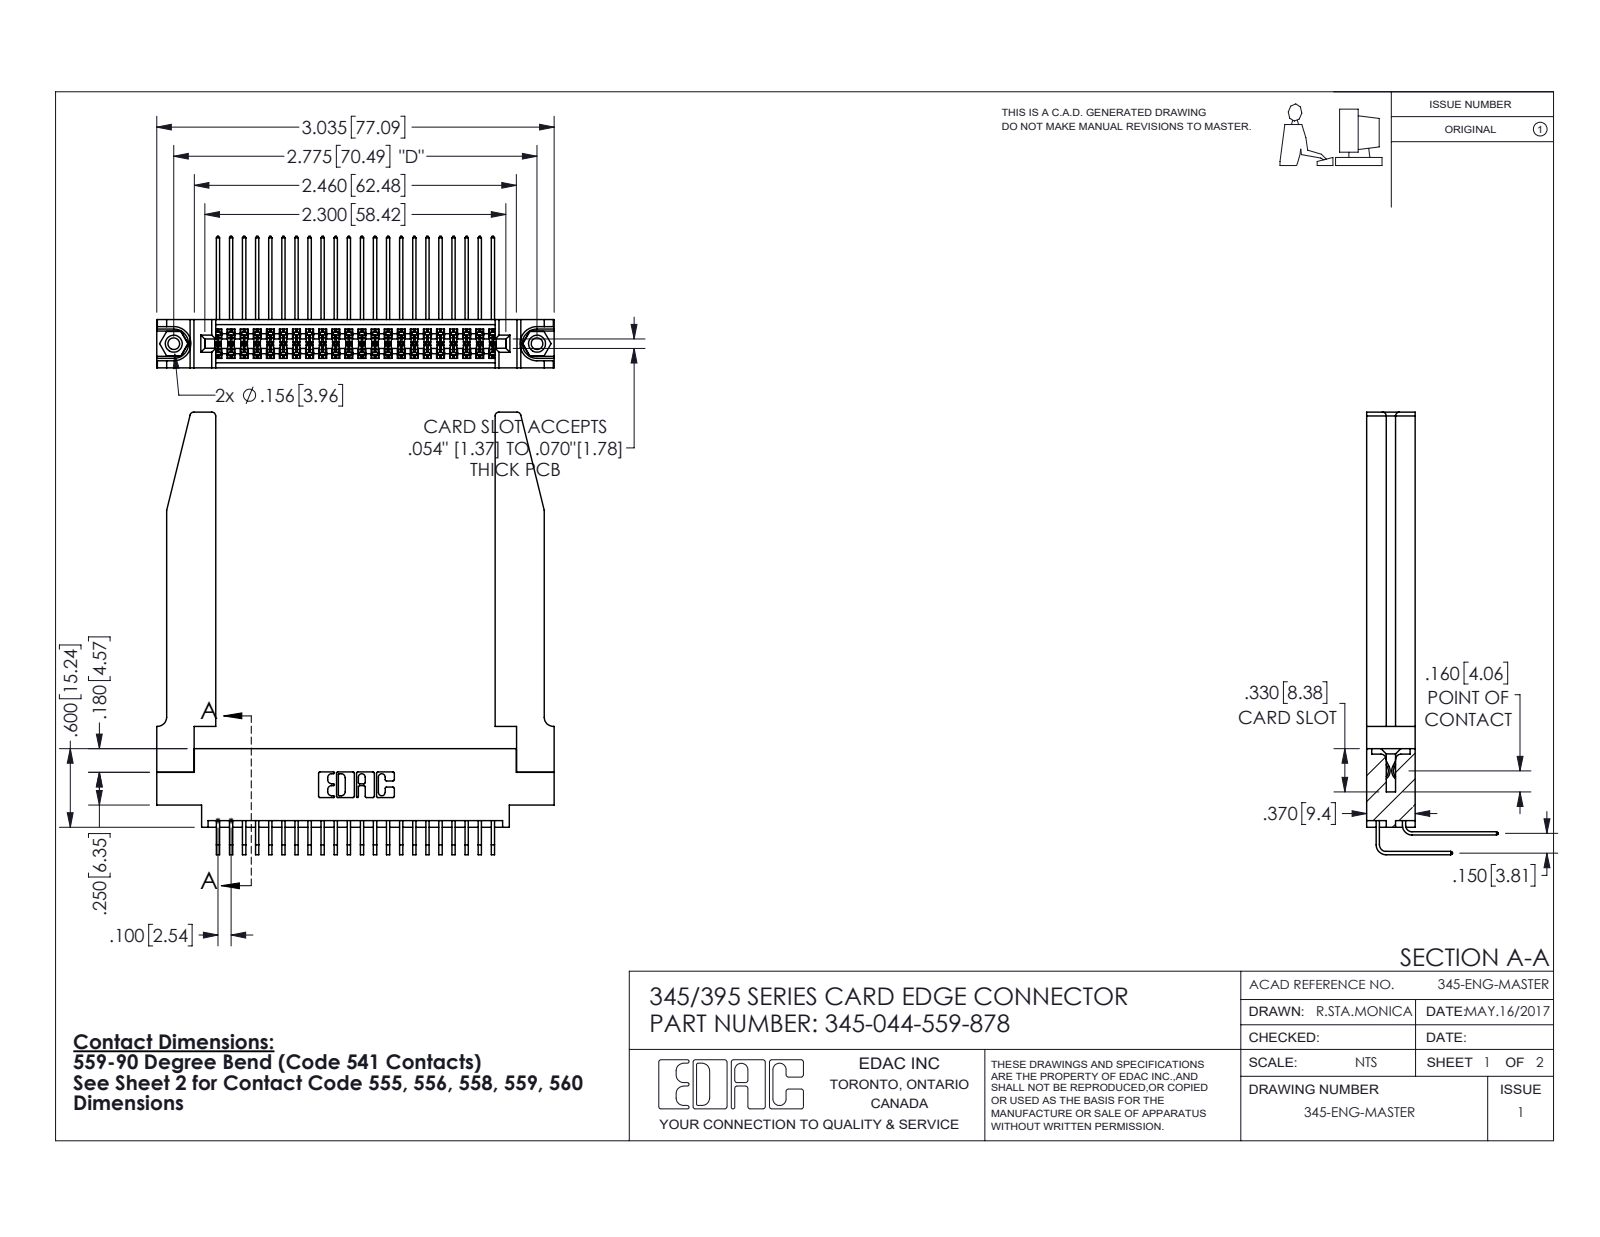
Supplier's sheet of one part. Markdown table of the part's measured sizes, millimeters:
| quantity | value |
| --- | --- |
| part name | 345-250-001_345-250-001-102; 345-292-001_559 Tail - 2; 345-044-559-878; 345 Part_0.170 Offset - 0.156 Dia-TH (+2 more) |
| STEP written by | SolidWorks 2016 (CONFIG_CONTROL_DESIGN) |
| units | millimeters |
| bodies | 49 solids, 2652 faces (1766 planar, 834 cylindrical, 52 other) |
| overall size | 85.8 × 77.1 × 25.5 |
| volume | 15 200 mm³ |
| surface area | 18 790 mm² |
| round holes (diameter × count) | 2.3 × 2, 3.2 × 2, 4 × 2, 1.6 × 1 |
| round bosses / shafts (diameter × count) | 3.9 × 2 |
| partial cylindrical surfaces (radius × count) | 0.2 × 87, 0.3 × 22, 0.8 × 8, 0.2 × 6, 0.8 × 6, 0.7 × 3, 0.4 × 2, 0.5 × 2 |
| main face-to-face distances | 9.4, 1.8, 7.6, 2.5, 6.9, 0.6, 5.1, 3.8, 5.7, 3.8 |
| hole center spacings | 6.9, 64.5, 70.5 |
